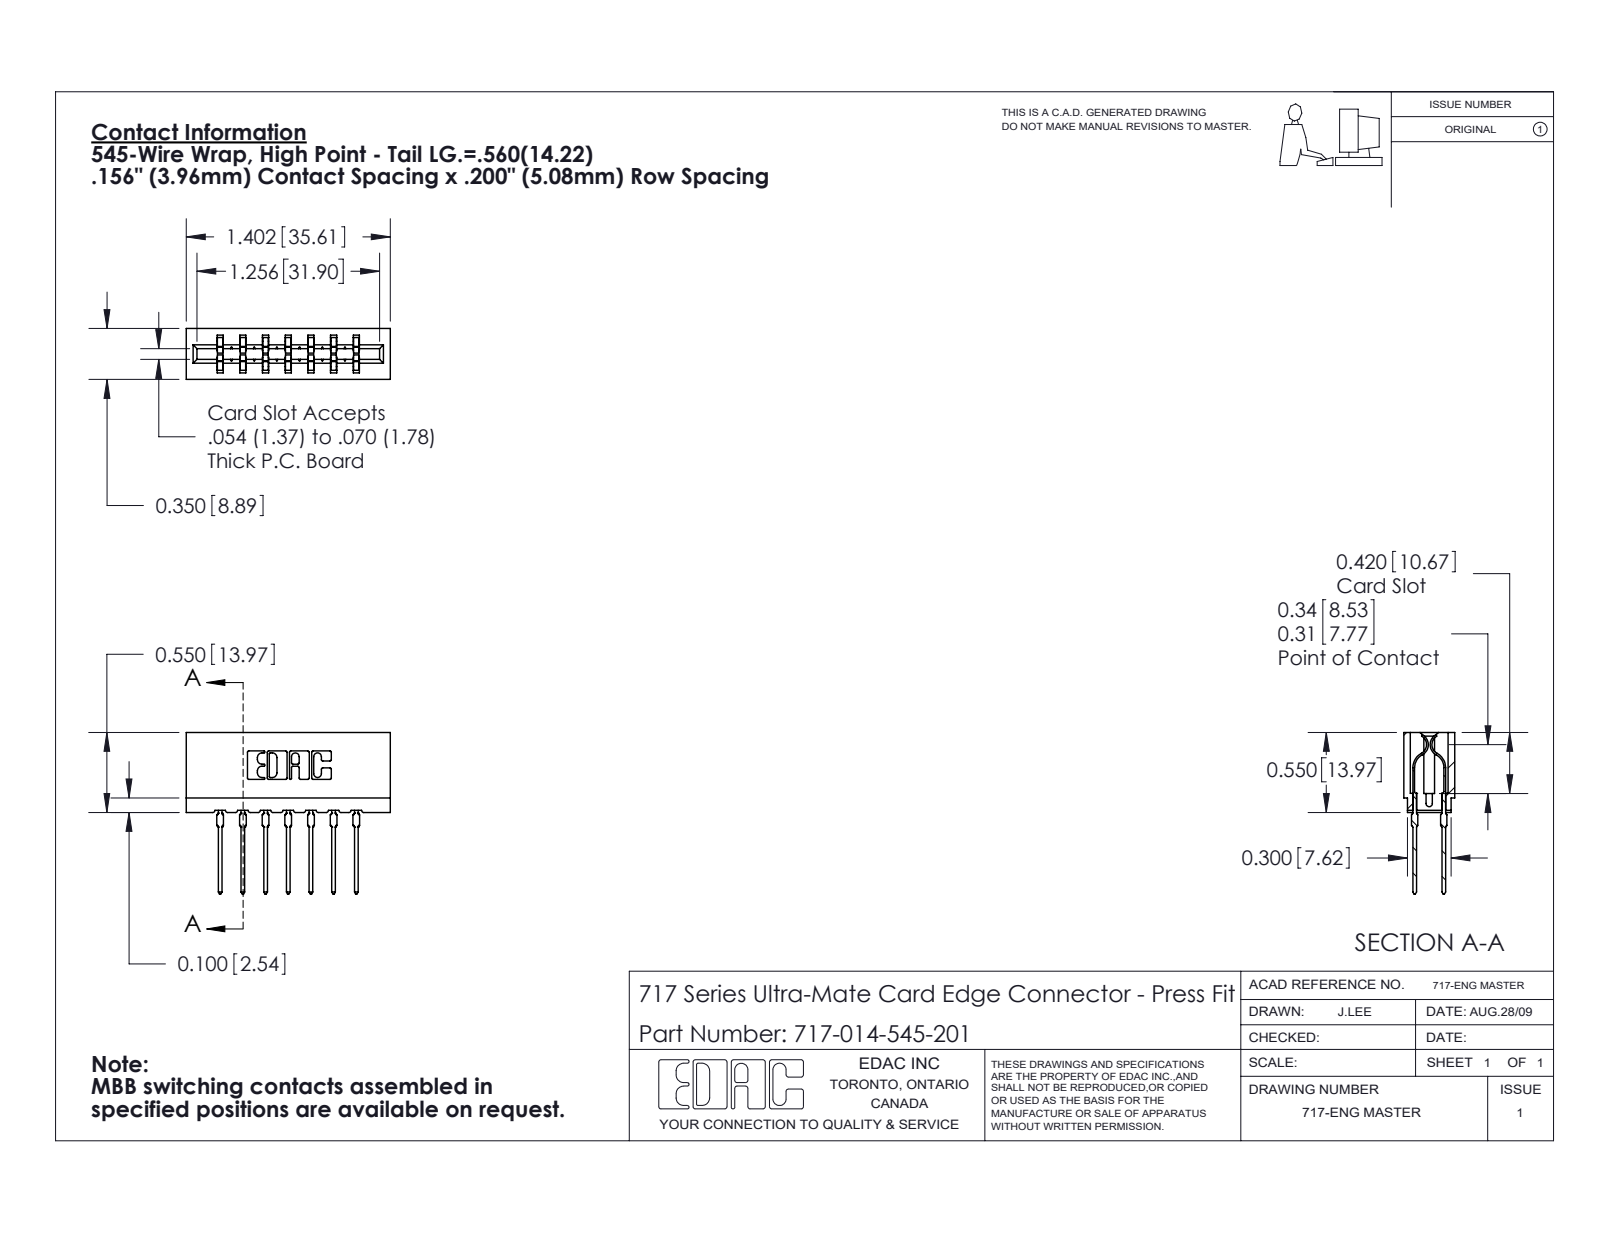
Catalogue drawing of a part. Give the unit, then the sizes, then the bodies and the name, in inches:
Units: inches
Overall size (bounding box): 1.402 × 1.109 × 0.35
Partial cylindrical surfaces — rounded edges, fillets, slot ends (radius × count): R0.021 ×28, R0.01 ×22, R0.015 ×14, R0.005 ×8, R0.011 ×8, R0.007 ×6, R0.031 ×6, R0.026 ×3
Main face-to-face distances: 0.212, 0.156, 0.138, 0.35, 0.198, 0.312, 0.468, 0.624, 0.063, 0.287
Volume: 0.2 in³ · Surface area: 7.416 in²
Bodies: 15 solids, 1354 faces (705 planar, 285 cylindrical, 364 other)
Part name (STEP PRODUCT): 717 Part_Insulator Option - 06; 717-014-545-201; 745-292-001_545
STEP written by: SolidWorks 2020 (CONFIG_CONTROL_DESIGN)
